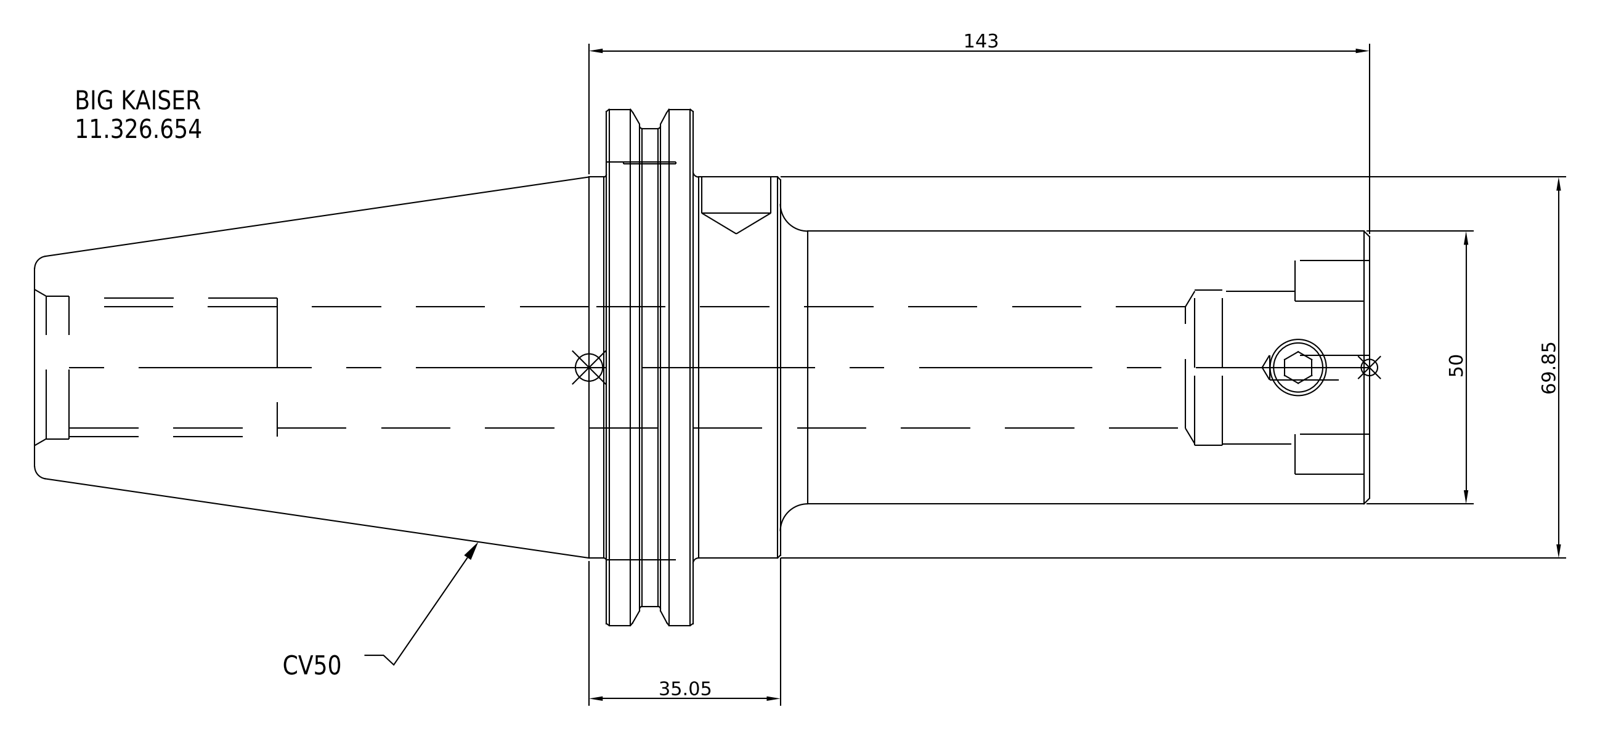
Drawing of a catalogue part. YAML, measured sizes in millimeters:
part_name: "11.326.654"
step_written_by: "SolidWorks 2021 (CONFIG_CONTROL_DESIGN)"
units: millimeters
bodies: {solids: 1, faces: 16, planar: 7, cylindrical: 6, other: 3}
overall_size: [244.6, 98.43, 98.43]
volume: 654538
surface_area: 57938
round_bosses_or_shafts:
  - {diameter: 98.43, count: 1}
  - {diameter: 91.29, count: 1}
  - {diameter: 69.85, count: 1}
  - {diameter: 50, count: 1}
face_to_face_distances: [17.55, 123.95, 141.5, 108, 15.95, 33.5, 244.6, 136.6, 120.65, 103.1]
